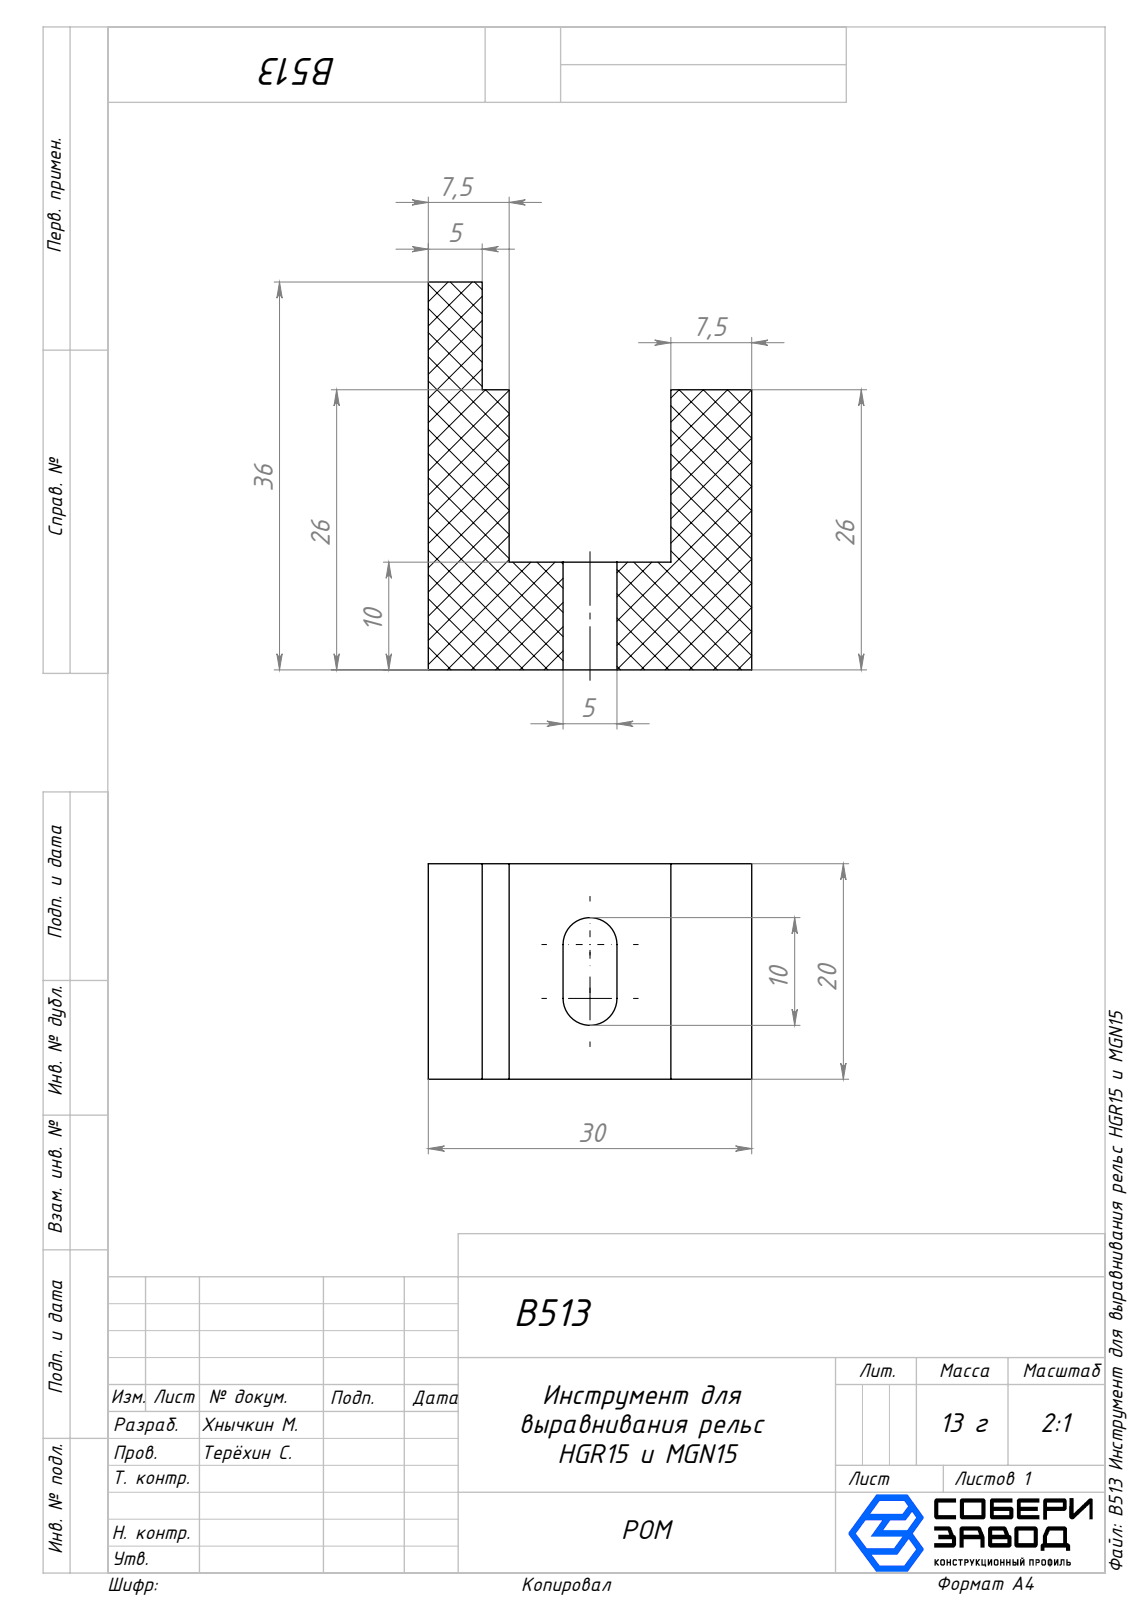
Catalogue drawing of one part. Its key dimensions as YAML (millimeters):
part_name: "B513 Инструмент для выравнивания рельс HGR15 и MGN15"
step_written_by: "SolidWorks 2025 (AUTOMOTIVE_DESIGN)"
units: millimeters
bodies: {solids: 1, faces: 16, planar: 14, cylindrical: 2, other: 0}
overall_size: [36, 30, 20]
volume: 11354
surface_area: 4628
partial_cylinders:
  - {radius: 2.5, count: 2}
face_to_face_distances: [7.5, 22.5, 20, 30, 10, 5, 15, 26, 17.5, 16]
